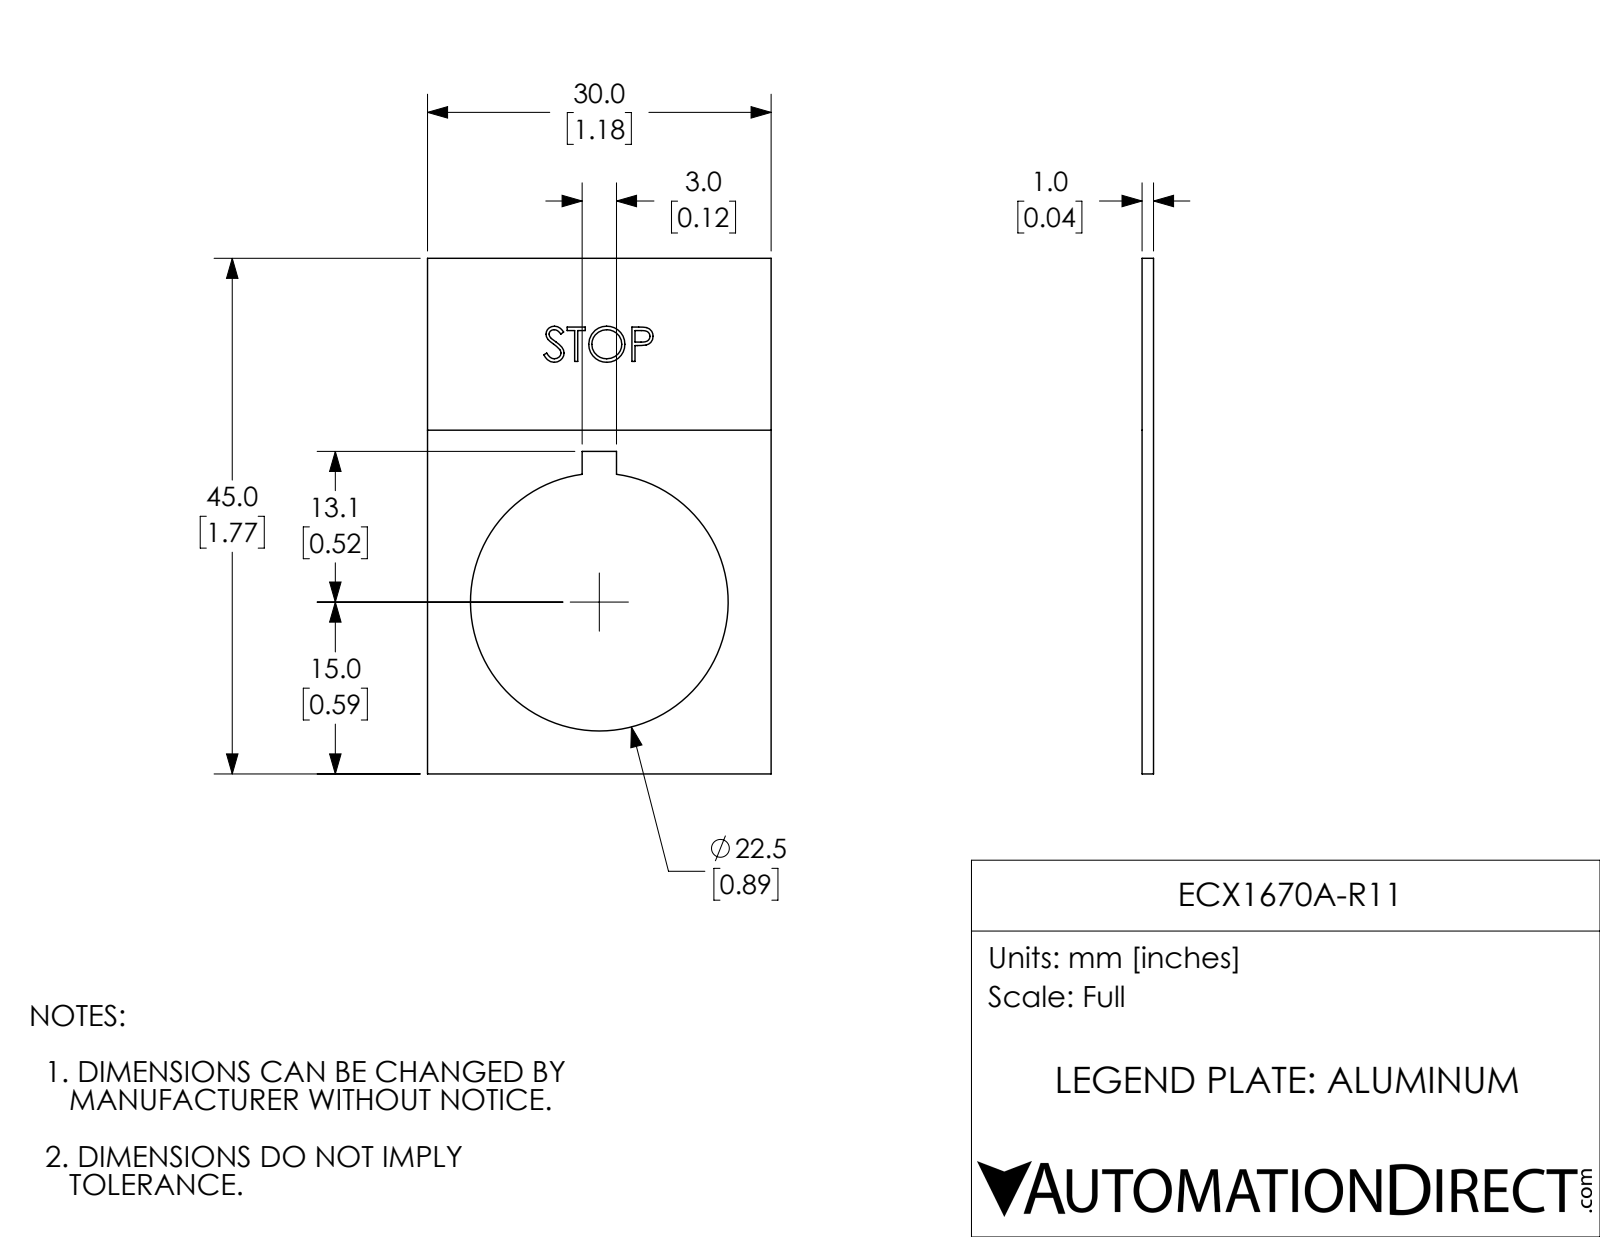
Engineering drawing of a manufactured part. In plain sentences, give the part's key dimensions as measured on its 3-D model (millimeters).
The part is named "ECX1670A-R11". Its 3-D file was written by "SolidWorks 2017 (AUTOMOTIVE_DESIGN)". It is 1 solid with 66 faces: 34 planar, 3 cylindrical and 29 other. Overall it measures 45 by 30 by 1 millimeters. Its volume is 950 cubic millimeters and its surface area 2 119 square millimeters. Round holes: 1 of diameter 22.5. The main face-to-face distances are 1, 30, 45, 1, 13.5, 16.5, 28.1, 16.8, 3, 5.
